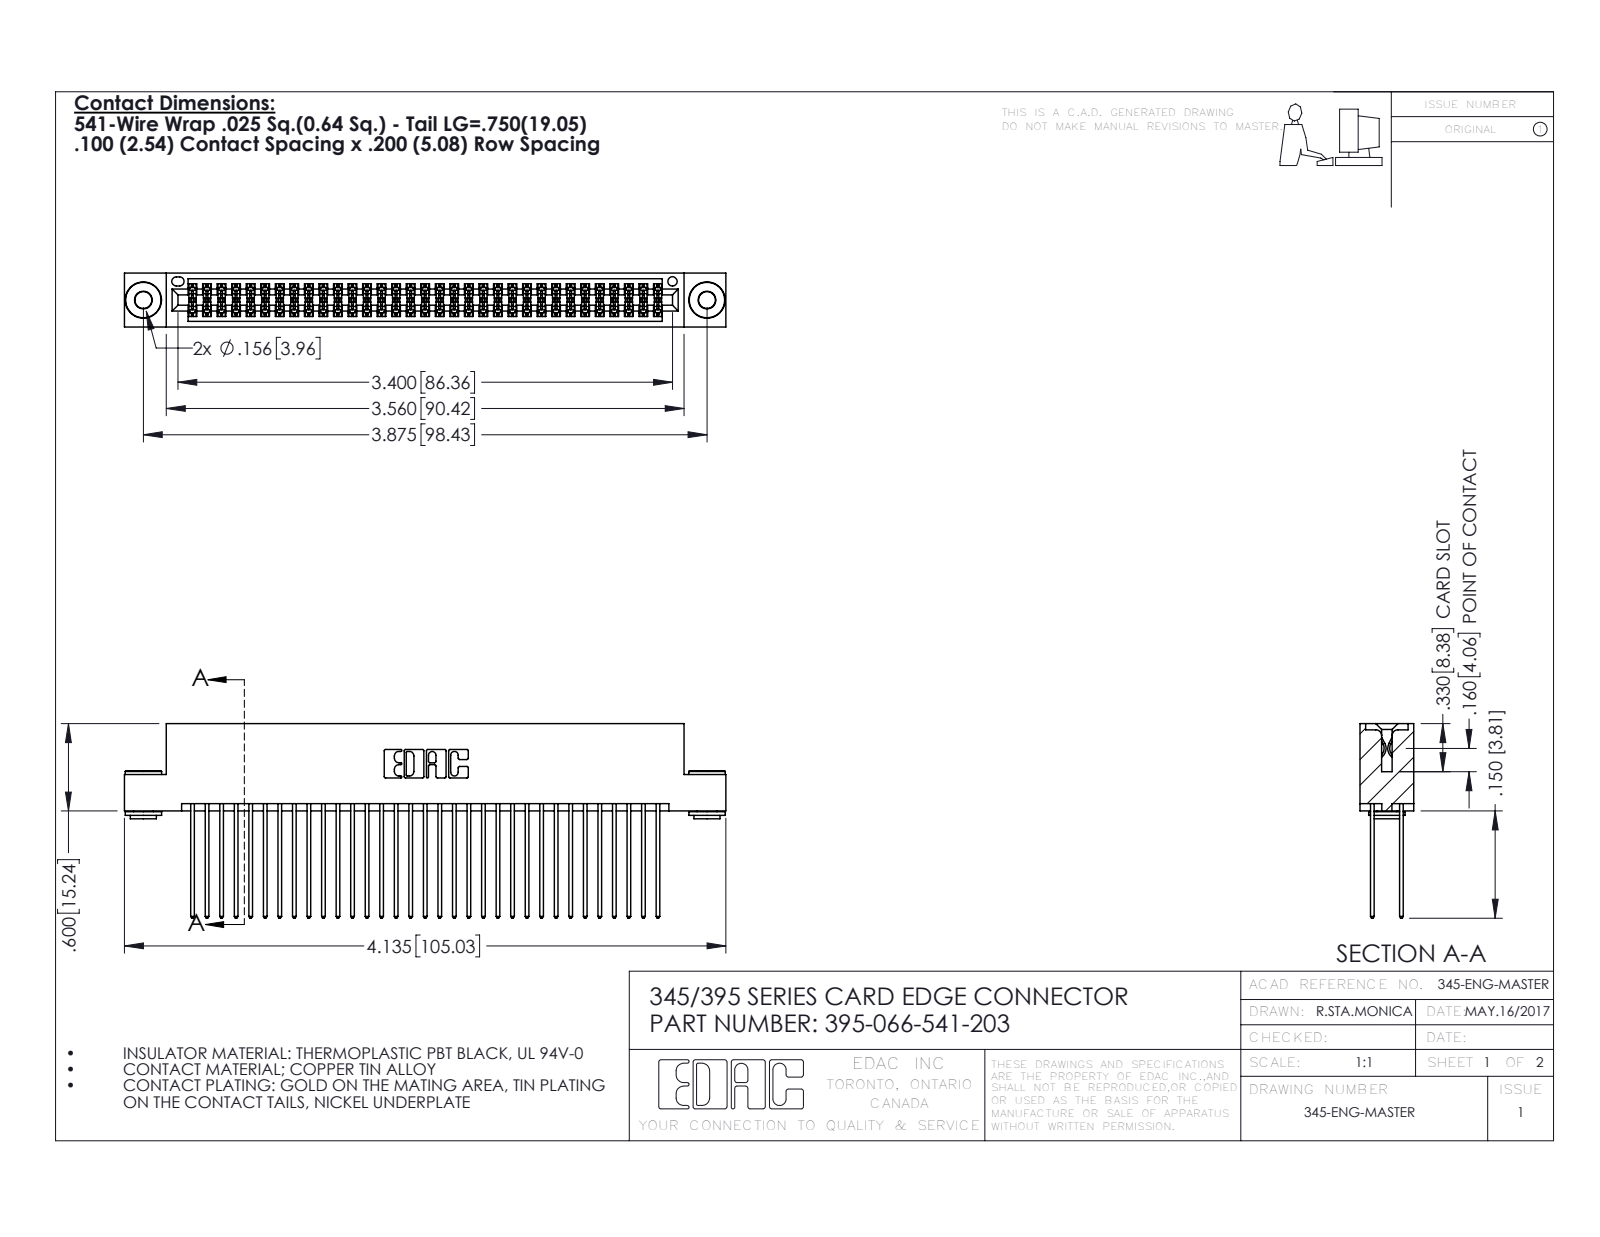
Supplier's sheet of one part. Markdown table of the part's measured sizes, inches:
| quantity | value |
| --- | --- |
| part name | 345-250-002_345-250-002-102; 395-066-541-203; 345 Part_Flush Mounting Lugs - 0.156 Dia-TH; 345-292-001_345-293-141 |
| STEP written by | SolidWorks 2016 (CONFIG_CONTROL_DESIGN) |
| units | inches |
| bodies | 69 solids, 3464 faces (2268 planar, 1188 cylindrical, 8 other) |
| overall size | 4.135 × 1.337 × 0.37 |
| volume | 0.642 in³ |
| surface area | 26.9 in² |
| round holes (diameter × count) | 0.116 × 2, 0.156 × 2, 0.064 × 1 |
| round bosses / shafts (diameter × count) | 0.25 × 2, 0.18 × 2, 0.136 × 2 |
| partial cylindrical surfaces (radius × count) | 0.006 × 99, 0.01 × 66, 0.01 × 22, 0.007 × 6, 0.031 × 6, 0.026 × 3, 0.014 × 2, 0.019 × 2 |
| main face-to-face distances | 0.072, 0.298, 0.2, 0.025, 0.098, 0.272, 0.225, 0.37, 0.175, 0.149 |
| hole center spacings | 0.27, 3.64, 3.875 |
